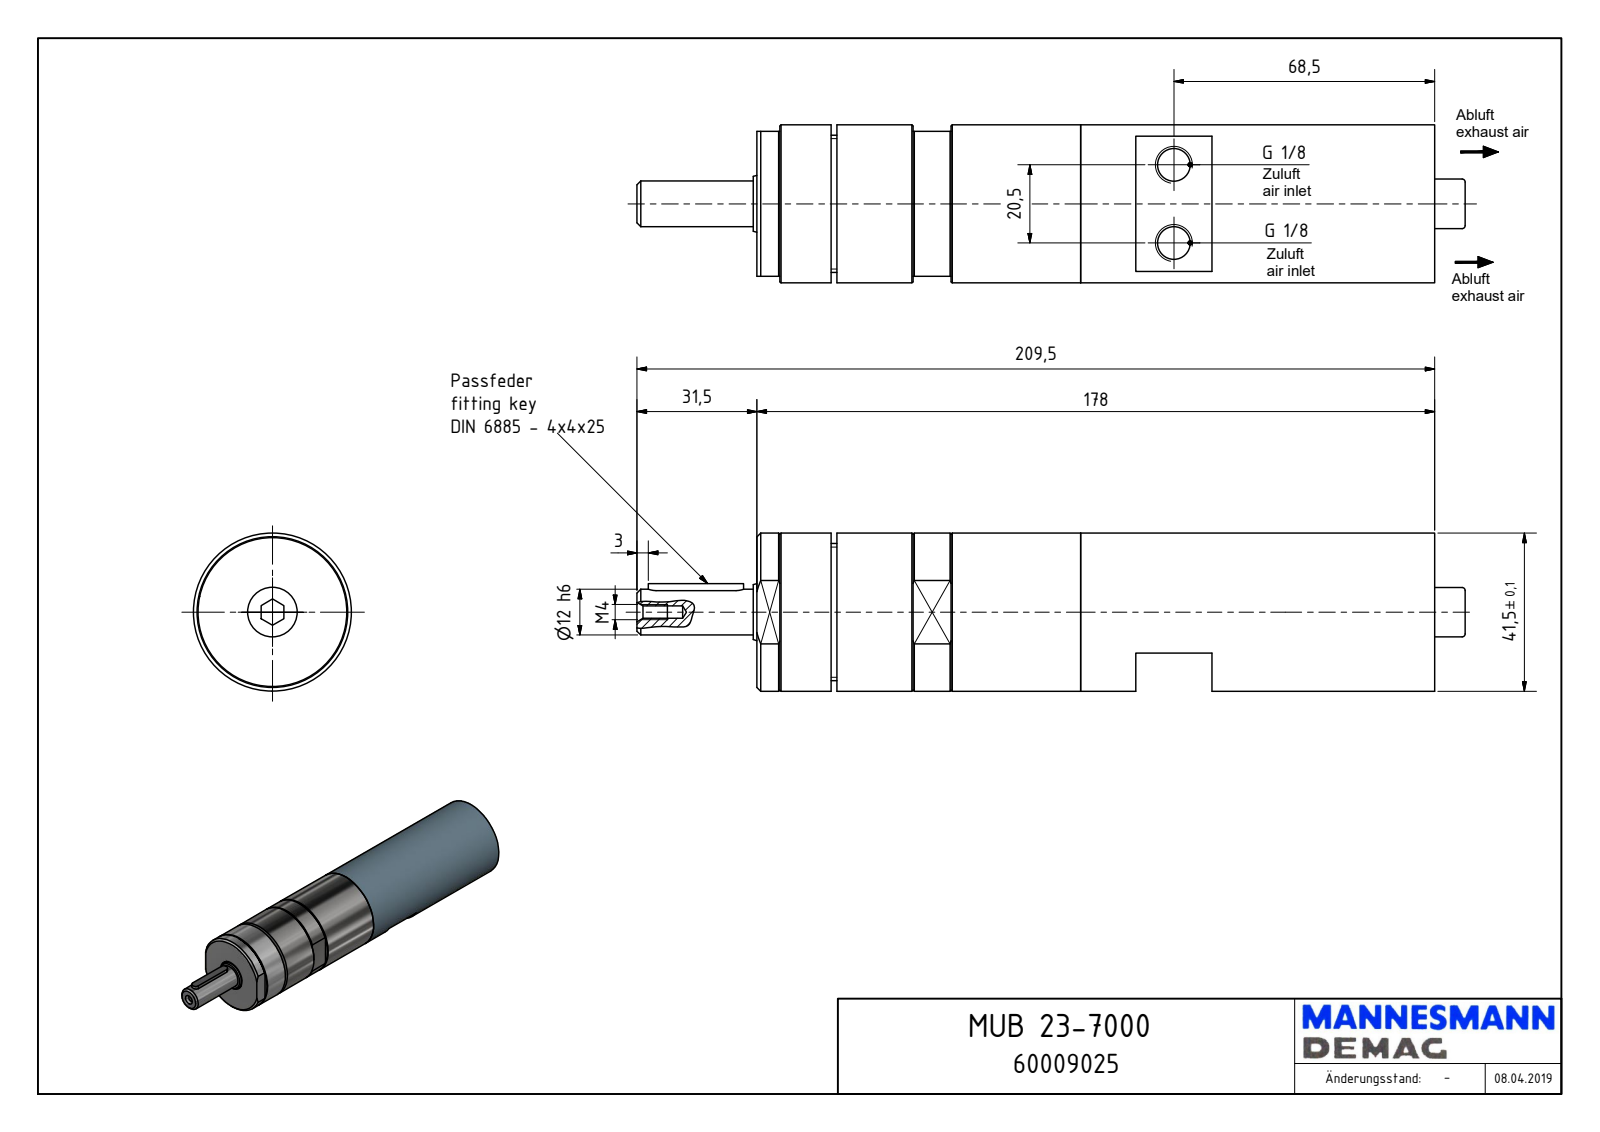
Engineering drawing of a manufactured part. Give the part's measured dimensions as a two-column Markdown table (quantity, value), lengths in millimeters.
| quantity | value |
| --- | --- |
| part name | MUB 23-7000_60009025 |
| STEP written by | Autodesk Inventor 2018 (AUTOMOTIVE_DESIGN) |
| units | millimeters |
| bodies | 1 solid, 133 faces (62 planar, 51 cylindrical, 20 other) |
| overall size | 217.5 × 41.5 × 41.5 |
| volume | 236 486 mm³ |
| surface area | 33 119 mm² |
| round holes (diameter × count) | 2 × 2, 4 × 2, 5 × 2, 8.57 × 2, 3.24 × 1, 8.5 × 1, 13 × 1, 16 × 1, 23 × 1, 39.5 × 1 |
| round bosses / shafts (diameter × count) | 41.5 × 1, 39.06 × 1, 39 × 1, 36 × 1, 14.95 × 1, 12 × 1, 8 × 1 |
| partial cylindrical surfaces (radius × count) | 1.6 × 2, 2 × 2, 4.5 × 1, 8.1 × 1, 11.2 × 1 |
| main face-to-face distances | 178, 78.5, 21, 1.5, 19.5, 158.5, 157, 98.5, 58.5, 20 |
| hole center spacings | 12.94, 20.5, 25 |
